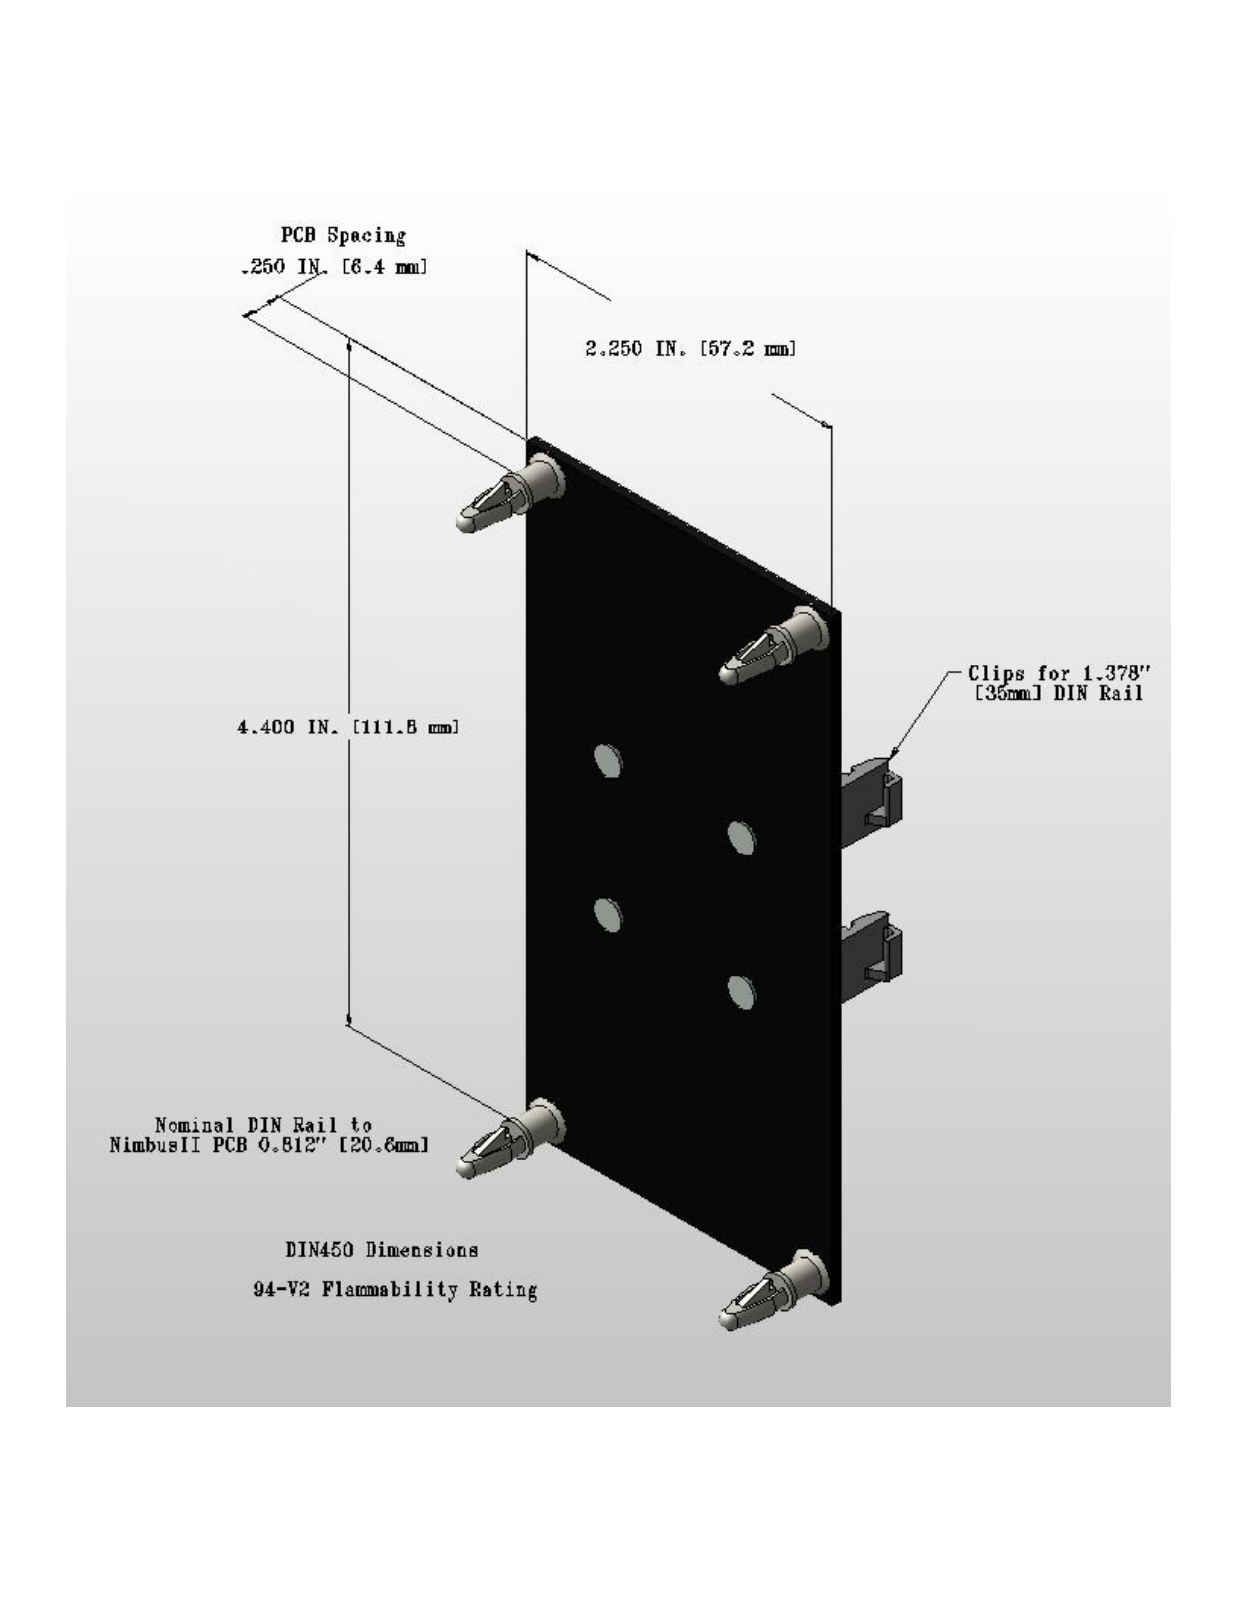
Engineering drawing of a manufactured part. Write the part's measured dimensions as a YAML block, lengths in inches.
step_written_by: "KeyCreator Pro (AP242_MANAGED_MODEL_BASED_3D_ENGINEERING_MIM_LF)"
units: inches
bodies: {solids: 11, faces: 536, planar: 310, cylindrical: 186, other: 40}
overall_size: [4.401, 2.25, 1.46]
volume: 1.01
surface_area: 35.82
round_holes:
  - {diameter: 0.156, count: 8}
  - {diameter: 0.108, count: 6}
  - {diameter: 0.079, count: 1}
  - {diameter: 0.118, count: 1}
round_bosses_or_shafts:
  - {diameter: 0.281, count: 4}
  - {diameter: 0.218, count: 4}
  - {diameter: 0.187, count: 4}
partial_cylinders:
  - {radius: 0.016, count: 20}
  - {radius: 0.039, count: 6}
  - {radius: 0.128, count: 6}
  - {radius: 0.02, count: 4}
  - {radius: 0.076, count: 4}
  - {radius: 0.079, count: 4}
  - {radius: 0.086, count: 4}
  - {radius: 0.02, count: 3}
face_to_face_distances: [0.062, 0.053, 0.984, 0.357, 0.295, 0.115, 0.242, 0.394, 0.984, 0.057]
hole_center_spacings: [0.984, 0.492, 1.1, 1.639, 1.844, 2.144, 2.596, 2.73]
